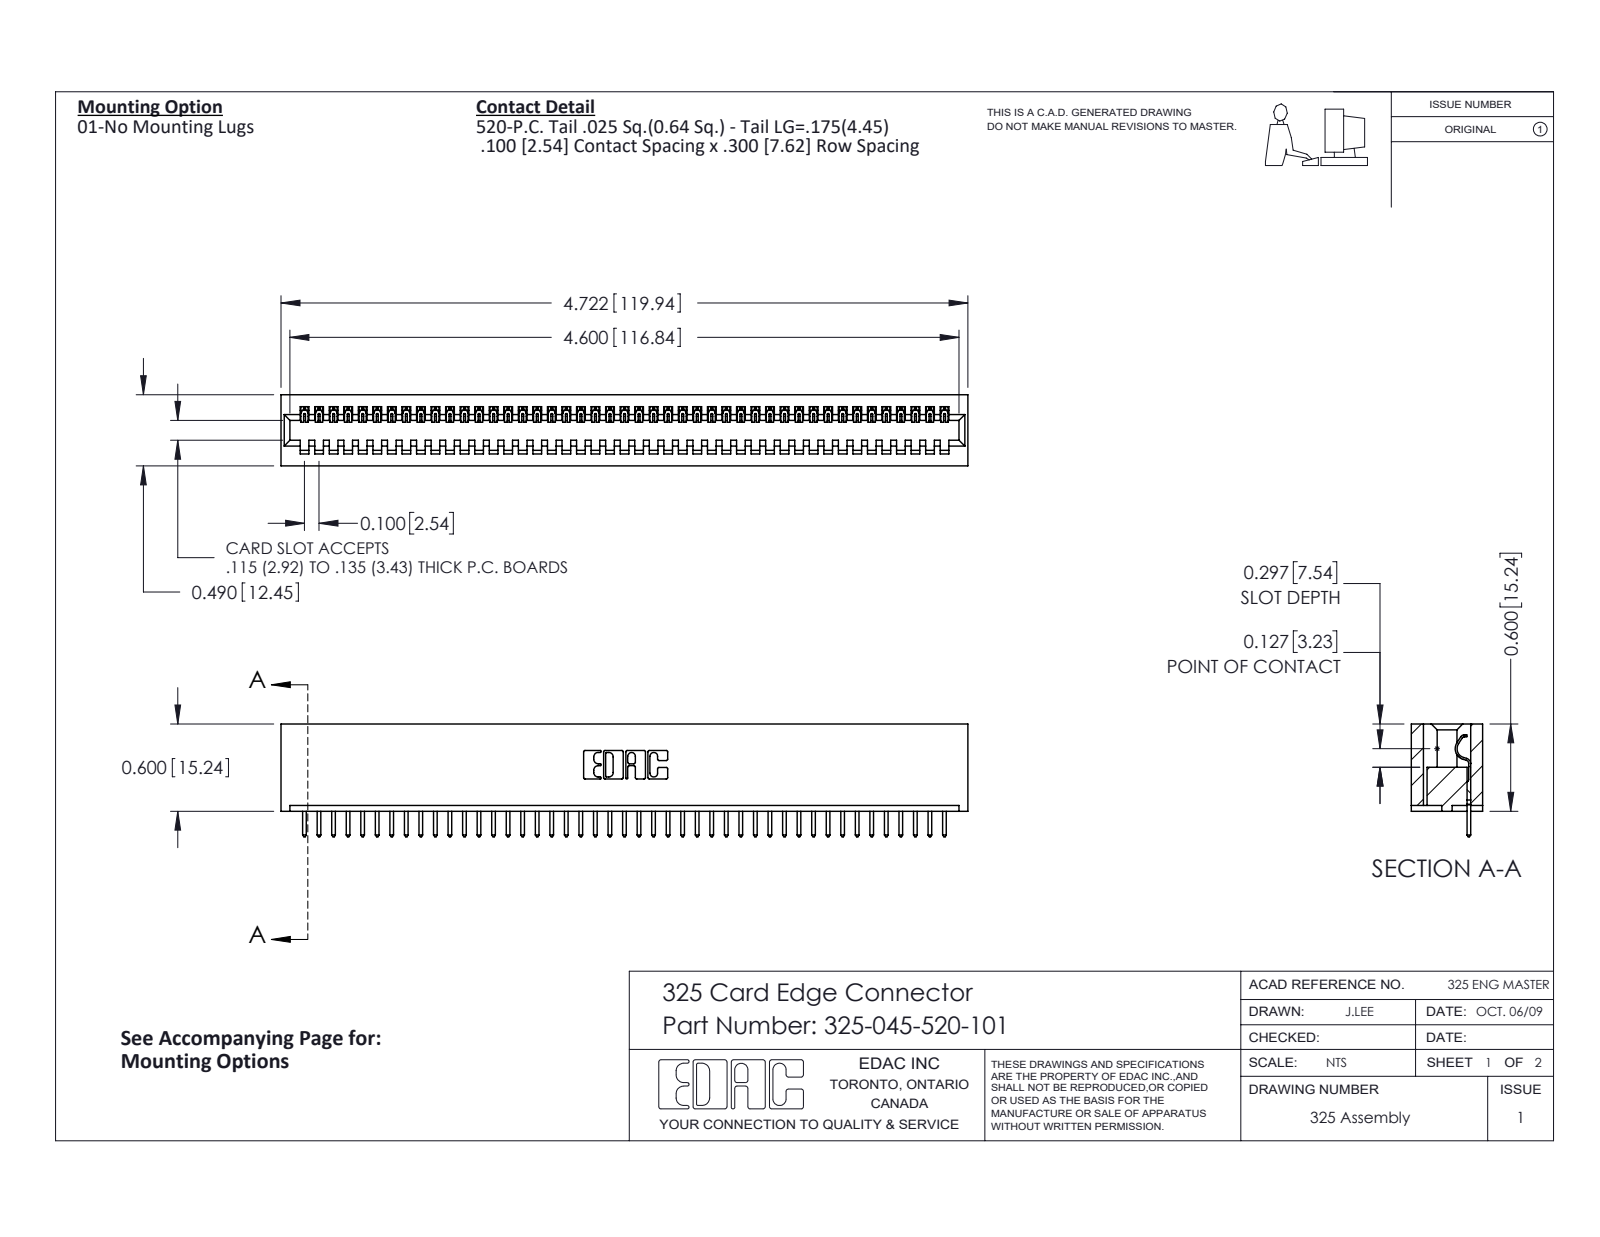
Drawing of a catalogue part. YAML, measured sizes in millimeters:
part_name: "325 Part_Lugless; 325-045-520-101; 325-292-001_325-293-120"
step_written_by: "SolidWorks 2016 (CONFIG_CONTROL_DESIGN)"
units: millimeters
bodies: {solids: 46, faces: 2716, planar: 1956, cylindrical: 760, other: 0}
overall_size: [119.9, 19.7, 12.4]
volume: 15700
surface_area: 17230
partial_cylinders:
  - {radius: 0.2, count: 90}
  - {radius: 0.3, count: 90}
  - {radius: 0.3, count: 22}
  - {radius: 0.2, count: 6}
  - {radius: 0.8, count: 6}
  - {radius: 0.7, count: 3}
  - {radius: 0.4, count: 1}
  - {radius: 0.6, count: 1}
face_to_face_distances: [2.1, 10.3, 12.4, 7.6, 2.7, 9.7, 0.6, 8.3, 14.2, 6.7]
